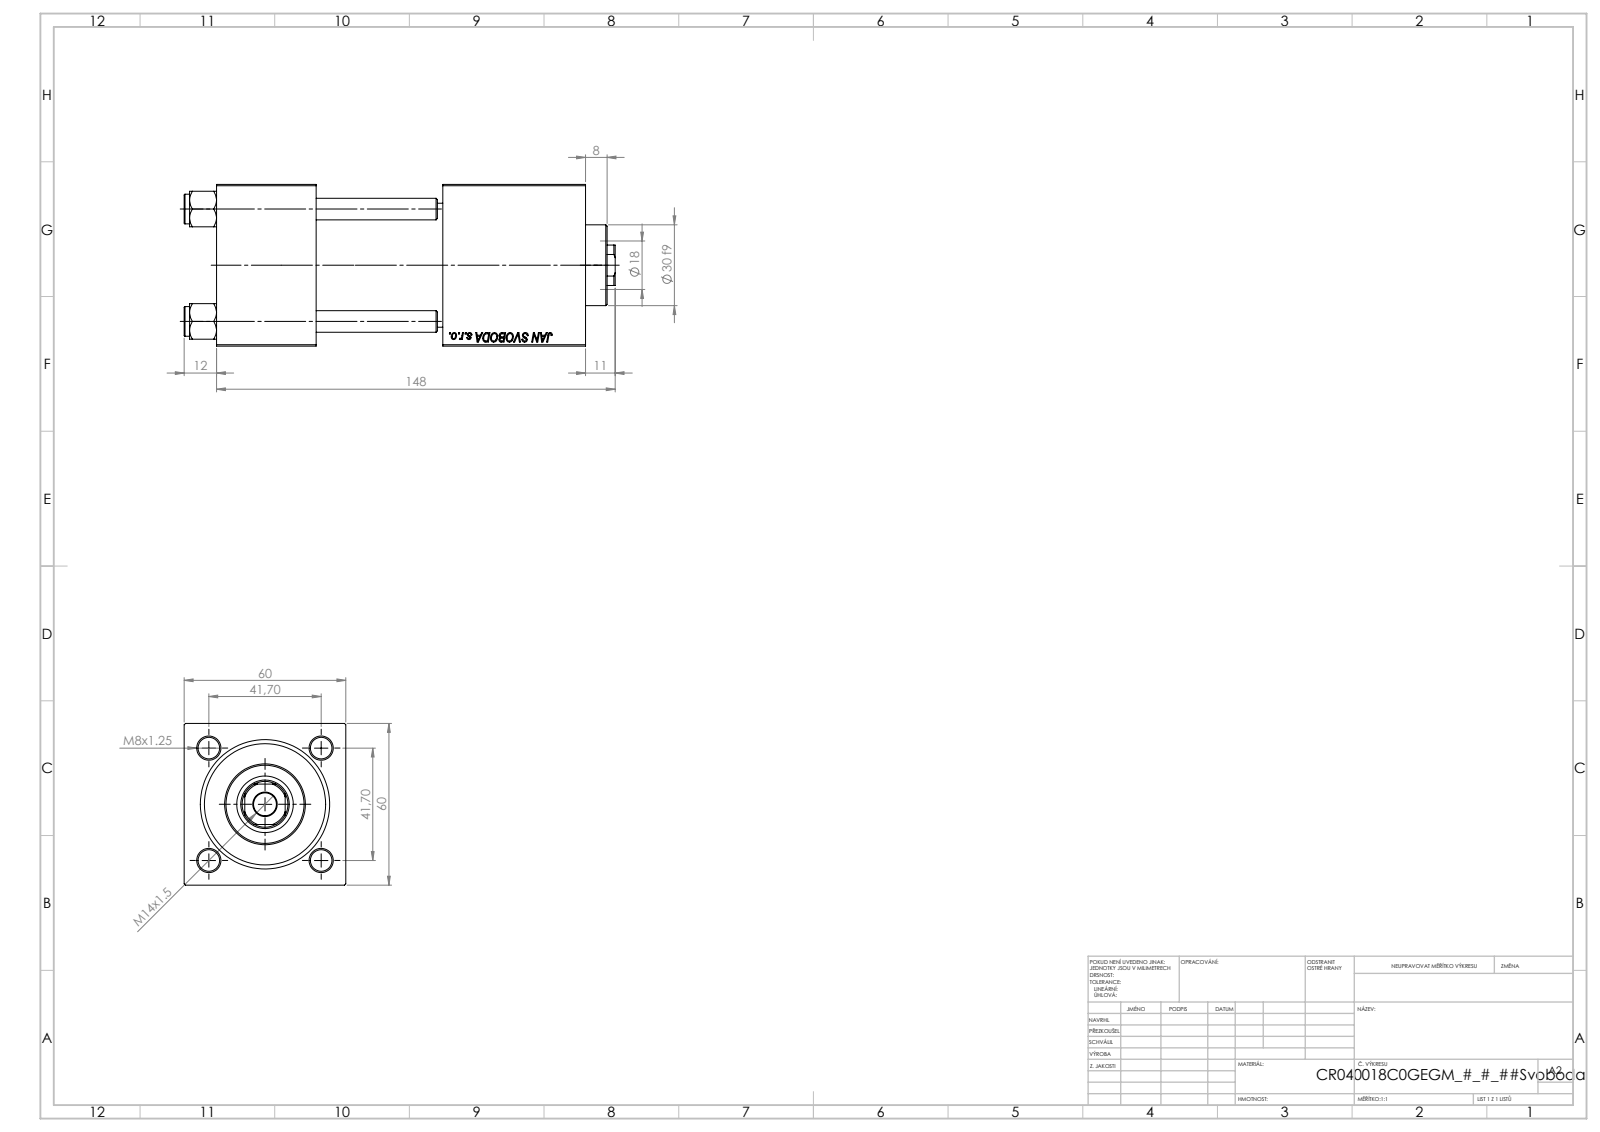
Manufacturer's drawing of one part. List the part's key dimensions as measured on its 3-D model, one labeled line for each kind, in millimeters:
Part name (STEP PRODUCT): V215_VC_A; V215CR_C_Body; V215CR_C_TYCINKA; NUT_M5_C (+1 more)
STEP written by: SolidWorks 2019 (CONFIG_CONTROL_DESIGN)
Units: millimetres
Bodies: 11 solids, 1149 faces (526 planar, 87 cylindrical, 536 other)
Overall size (bounding box): 160 × 60 × 60
Volume: 375 016 mm³ · Surface area: 97 368 mm²
Round holes (diameter × count): ⌀8 ×4, ⌀7 ×2, ⌀16.66 ×2, ⌀24 ×2, ⌀8.5 ×1, ⌀18 ×1, ⌀21 ×1, ⌀31 ×1, ⌀40 ×1, ⌀45 ×1
Round bosses / shafts (diameter × count): ⌀11 ×4, ⌀46 ×1, ⌀30 ×1
Partial cylindrical surfaces — rounded edges, fillets, slot ends (radius × count): R8.5 ×1
Main face-to-face distances: 60, 37, 137, 53, 100, 47, 84, 108.3, 71.3, 24.3
Hole centre spacings: 29.49, 41.7, 58.97, 81.5
